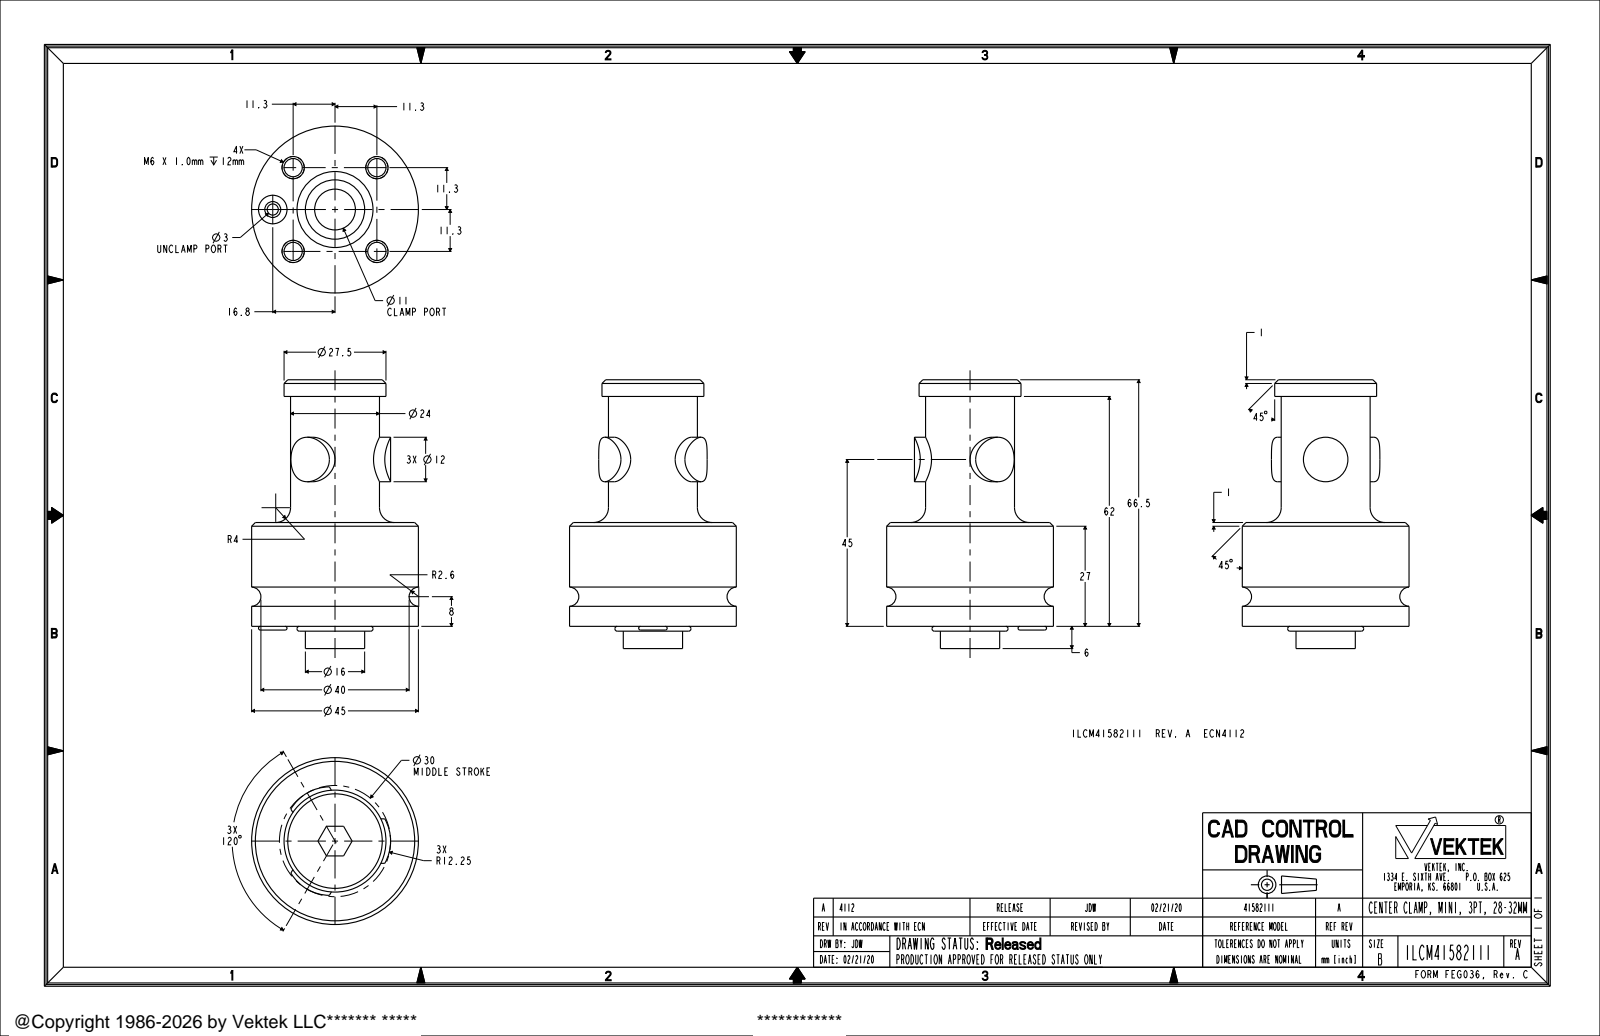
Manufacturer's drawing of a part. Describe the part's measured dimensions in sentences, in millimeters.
The part is named "ILCM41582111". Its 3-D file was written by "PRO/ENGINEER BY PARAMETRIC TECHNOLOGY CORPORATION, 2013320 (AUTOMOTIVE_DESIGN)". It is 1 solid with 105 faces: 26 planar, 43 cylindrical and 36 other. Overall it measures 72.5 by 45 by 45 millimeters. Its volume is 61 872 cubic millimeters and its surface area 13 616 square millimeters. Round holes: 4 of diameter 4.92, 1 of diameter 3, 1 of diameter 11. Round bosses or shafts: 4 of diameter 6, 3 of diameter 12, 1 of diameter 45, 1 of diameter 27.5, 1 of diameter 24, 1 of diameter 20.5, 1 of diameter 16. Partial cylindrical surfaces (rounded edges, fillets, slot ends): 3 of radius 12.25. The main face-to-face distances are 28, 66.5, 38.5, 34, 6, 62, 4.5, 1, 29, 63. The hole center spacings are 15.98, 22.6, 12.57, 30.29, 31.96, 16.8.
